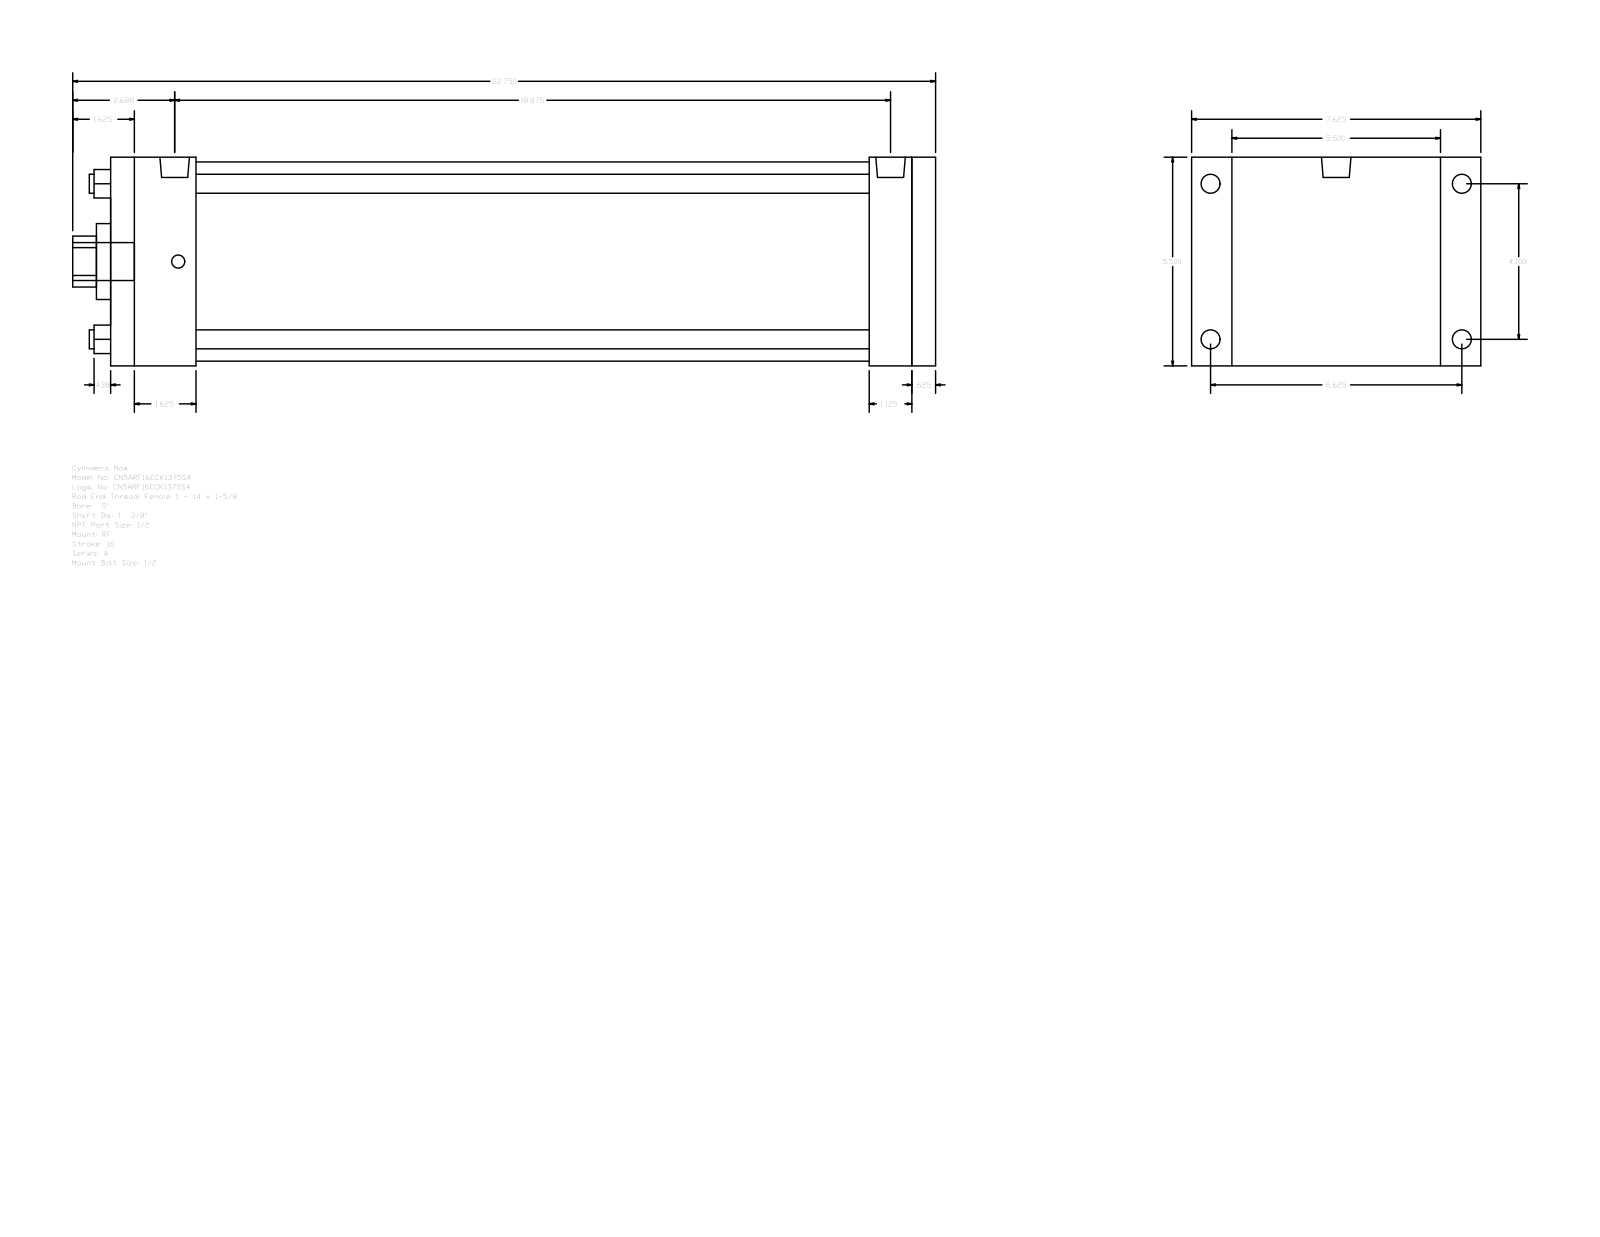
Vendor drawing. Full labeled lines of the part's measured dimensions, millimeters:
Part name (STEP PRODUCT): A_RF__0500_1.375
STEP written by: GSSL Pune (CONFIG_CONTROL_DESIGN)
Units: millimetres
Bodies: 0 solids, 92 faces (64 planar, 28 cylindrical, 0 other)
Overall size (bounding box): 577.85 × 193.68 × 139.7
Round holes (diameter × count): ⌀12.7 ×4, ⌀34.92 ×1, ⌀50.8 ×1, ⌀133.35 ×1
Round bosses / shafts (diameter × count): ⌀12.7 ×4, ⌀8.73 ×4, ⌀19.77 ×2, ⌀25.4 ×1
Partial cylindrical surfaces — rounded edges, fillets, slot ends (radius × count): R17.06 ×1
Main face-to-face distances: 139.7, 552.45, 15.87, 536.58, 28.58, 57.15, 479.43, 495.3, 508, 450.85
Hole centre spacings: 73.64, 104.14, 147.28
